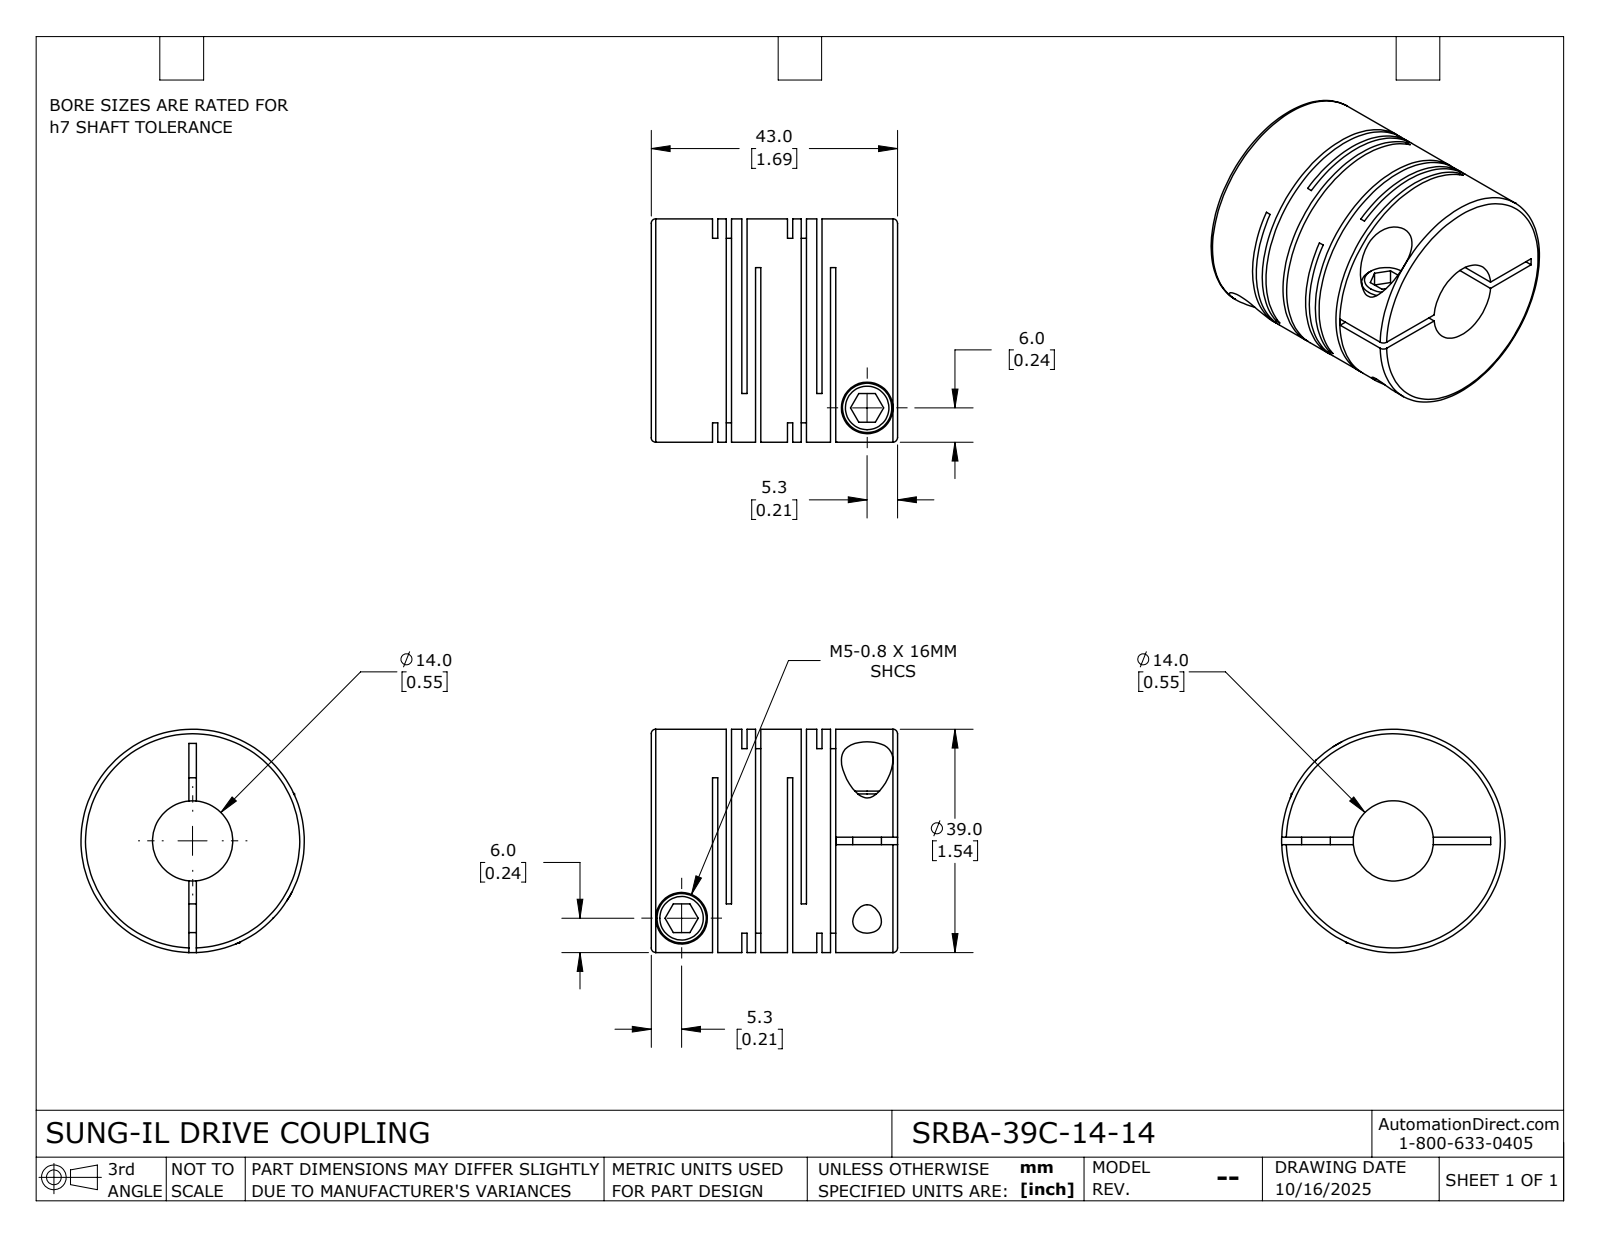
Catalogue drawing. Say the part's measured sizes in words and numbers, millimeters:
The part is named "SRBA-39C-14-14". Its 3-D file was written by "SolidWorks 2024 (CONFIG_CONTROL_DESIGN)". It is 1 solid with 115 faces: 60 planar, 42 cylindrical and 13 other. Overall it measures 43 by 39 by 39 millimeters. Its volume is 36 987 cubic millimeters and its surface area 23 652 square millimeters. Round holes: 2 of diameter 5, 2 of diameter 9, 1 of diameter 14. Round bosses or shafts: 2 of diameter 8.6, 1 of diameter 39. The main face-to-face distances are 13.1, 0.92, 2.4, 5.1, 10.7, 14.02, 18.2, 12.18, 1.48, 4.18.
